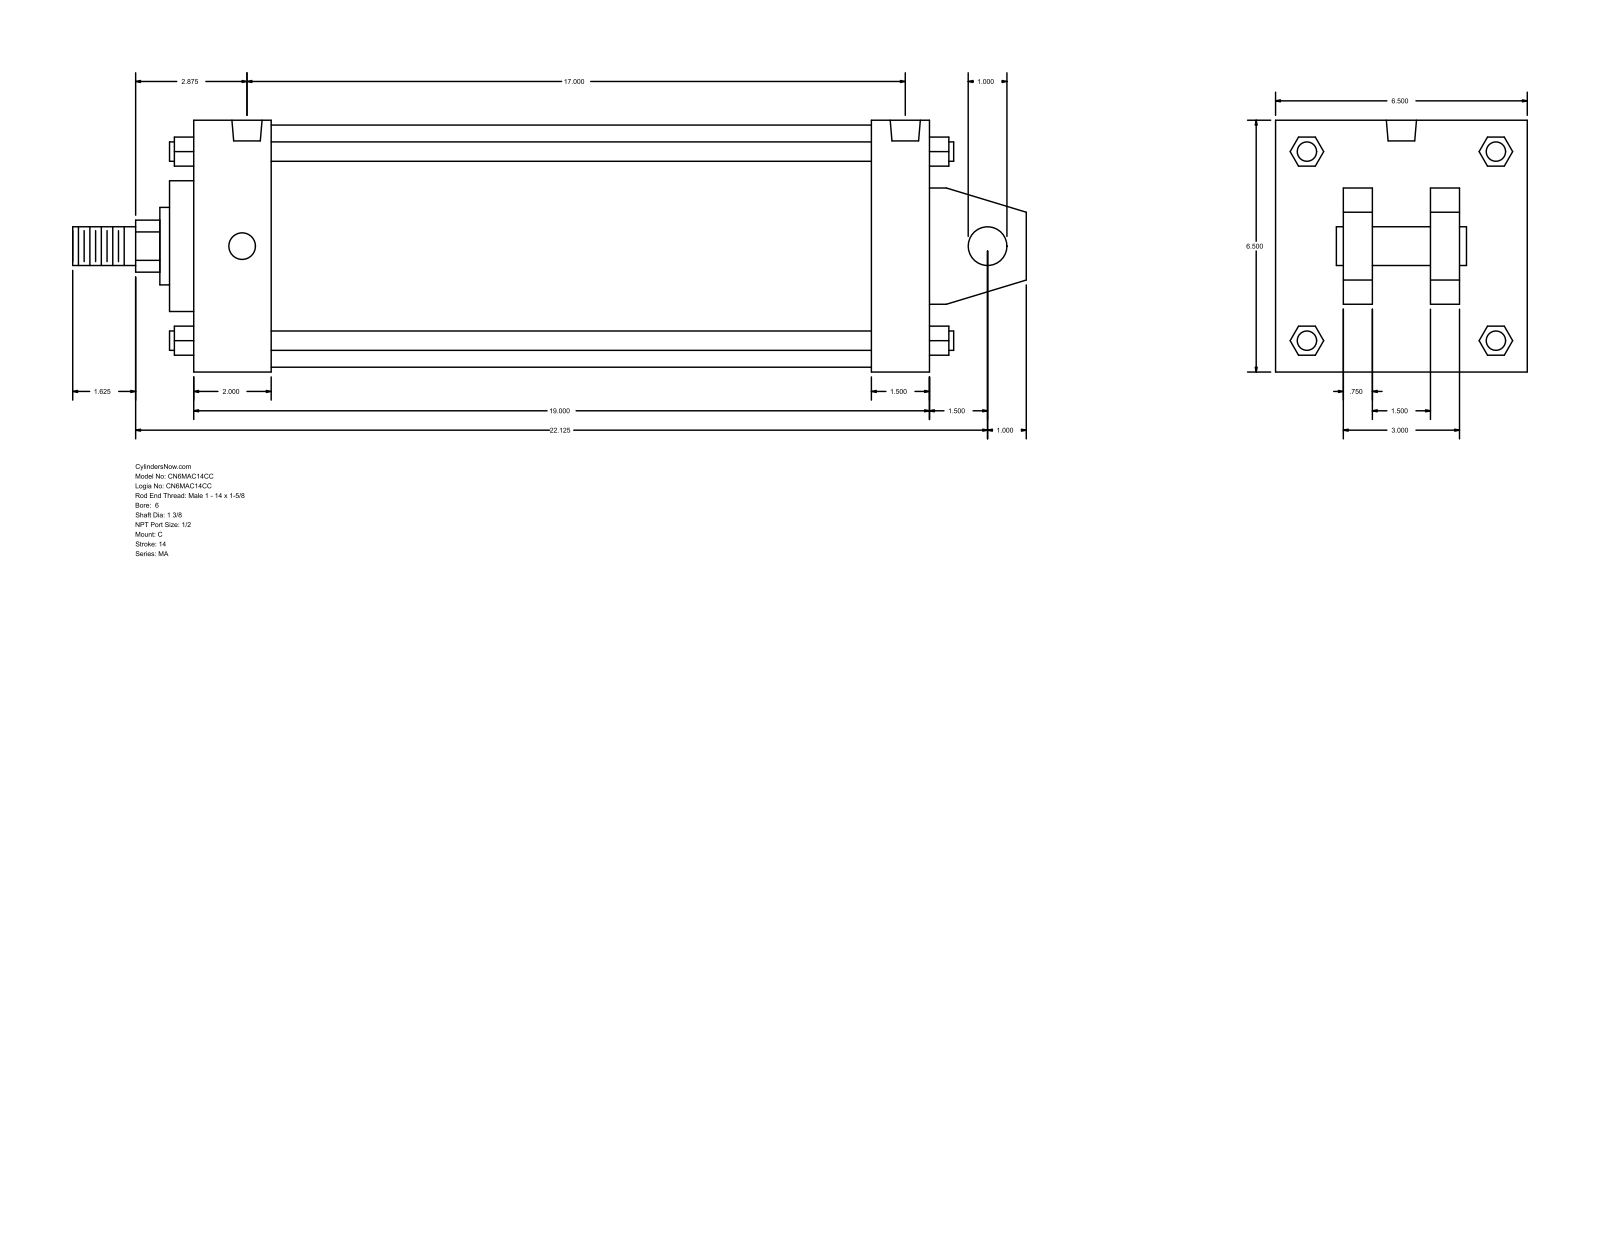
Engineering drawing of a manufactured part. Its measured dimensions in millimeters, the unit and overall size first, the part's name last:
Units: millimetres
Overall size (bounding box): 625.48 × 165.1 × 165.1
Round holes (diameter × count): ⌀17.46 ×4, ⌀19.77 ×2
Round bosses / shafts (diameter × count): ⌀12.7 ×4, ⌀25.4 ×2, ⌀158.75 ×1, ⌀85.72 ×1, ⌀50.8 ×1, ⌀34.92 ×1
Partial cylindrical surfaces — rounded edges, fillets, slot ends (radius × count): R17.06 ×1
Main face-to-face distances: 165.1, 482.6, 38.1, 19.05, 63.5, 101.6, 50.8, 44.45, 120.65, 444.5
Hole centre spacings: 431.8, 3.17, 3.18, 428.62, 431.79, 434.97
Bodies: 0 solids, 141 faces (109 planar, 32 cylindrical, 0 other)
Part name (STEP PRODUCT): MA_C__0600_1.375
STEP written by: GSSL Pune (CONFIG_CONTROL_DESIGN)
